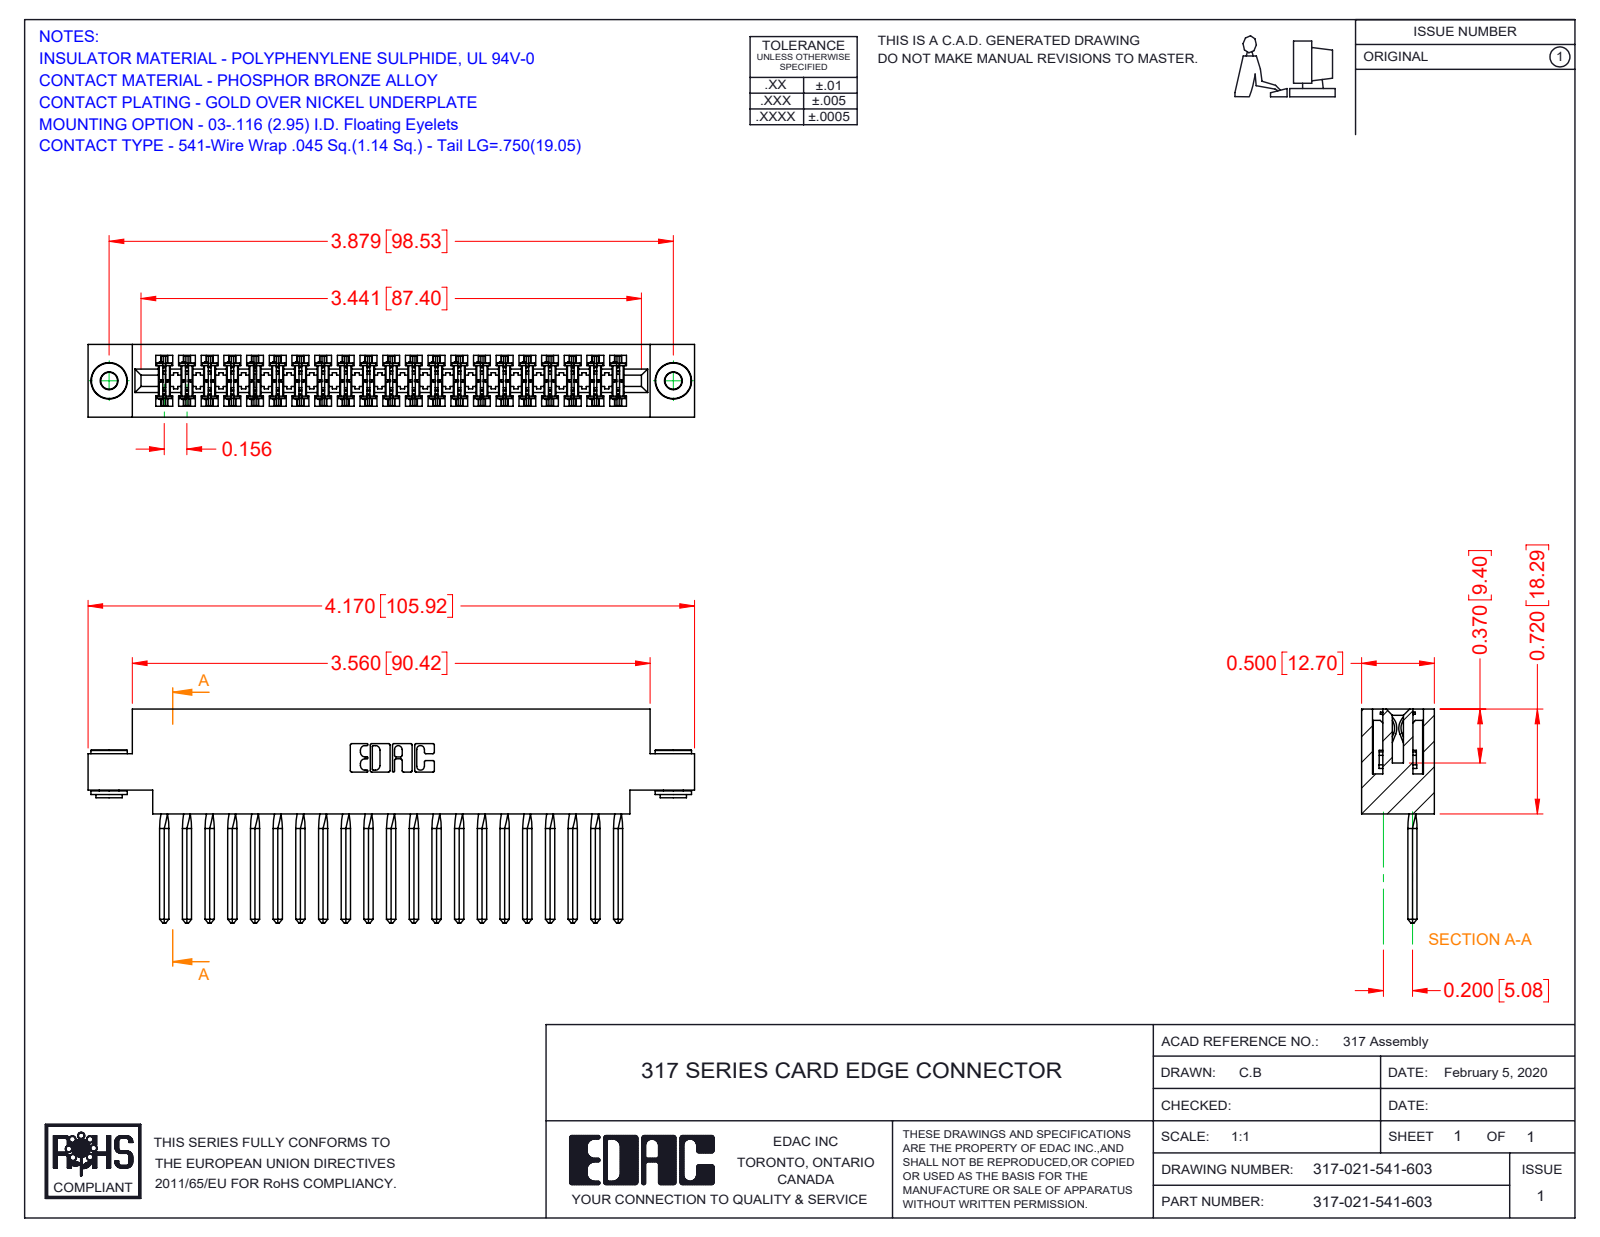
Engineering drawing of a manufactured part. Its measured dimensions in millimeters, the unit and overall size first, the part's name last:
Units: millimetres
Overall size (bounding box): 105.9 × 37.3 × 12.7
Round holes (diameter × count): ⌀2.9 ×2, ⌀4 ×2
Round bosses / shafts (diameter × count): ⌀6.4 ×2, ⌀4.6 ×2, ⌀3.5 ×2
Partial cylindrical surfaces — rounded edges, fillets, slot ends (radius × count): R0.4 ×42, R0.3 ×22, R0.2 ×6, R0.8 ×6, R0.7 ×3, R2.4 ×2, R2.5 ×2, R2.8 ×2
Main face-to-face distances: 12.7, 1.9, 10.8, 2.8, 8.9, 5, 19.6, 5.6, 16.8, 18.3
Hole centre spacings: 98.5
Volume: 16 550 mm³ · Surface area: 22 900 mm²
Bodies: 24 solids, 3332 faces (2672 planar, 568 cylindrical, 92 other)
Part name (STEP PRODUCT): 345-250-002_345-250-002-102; 317 Part_.156 Dia - TH; 317-021-541-603; 317-290-002_541
STEP written by: SolidWorks 2016 (CONFIG_CONTROL_DESIGN)
